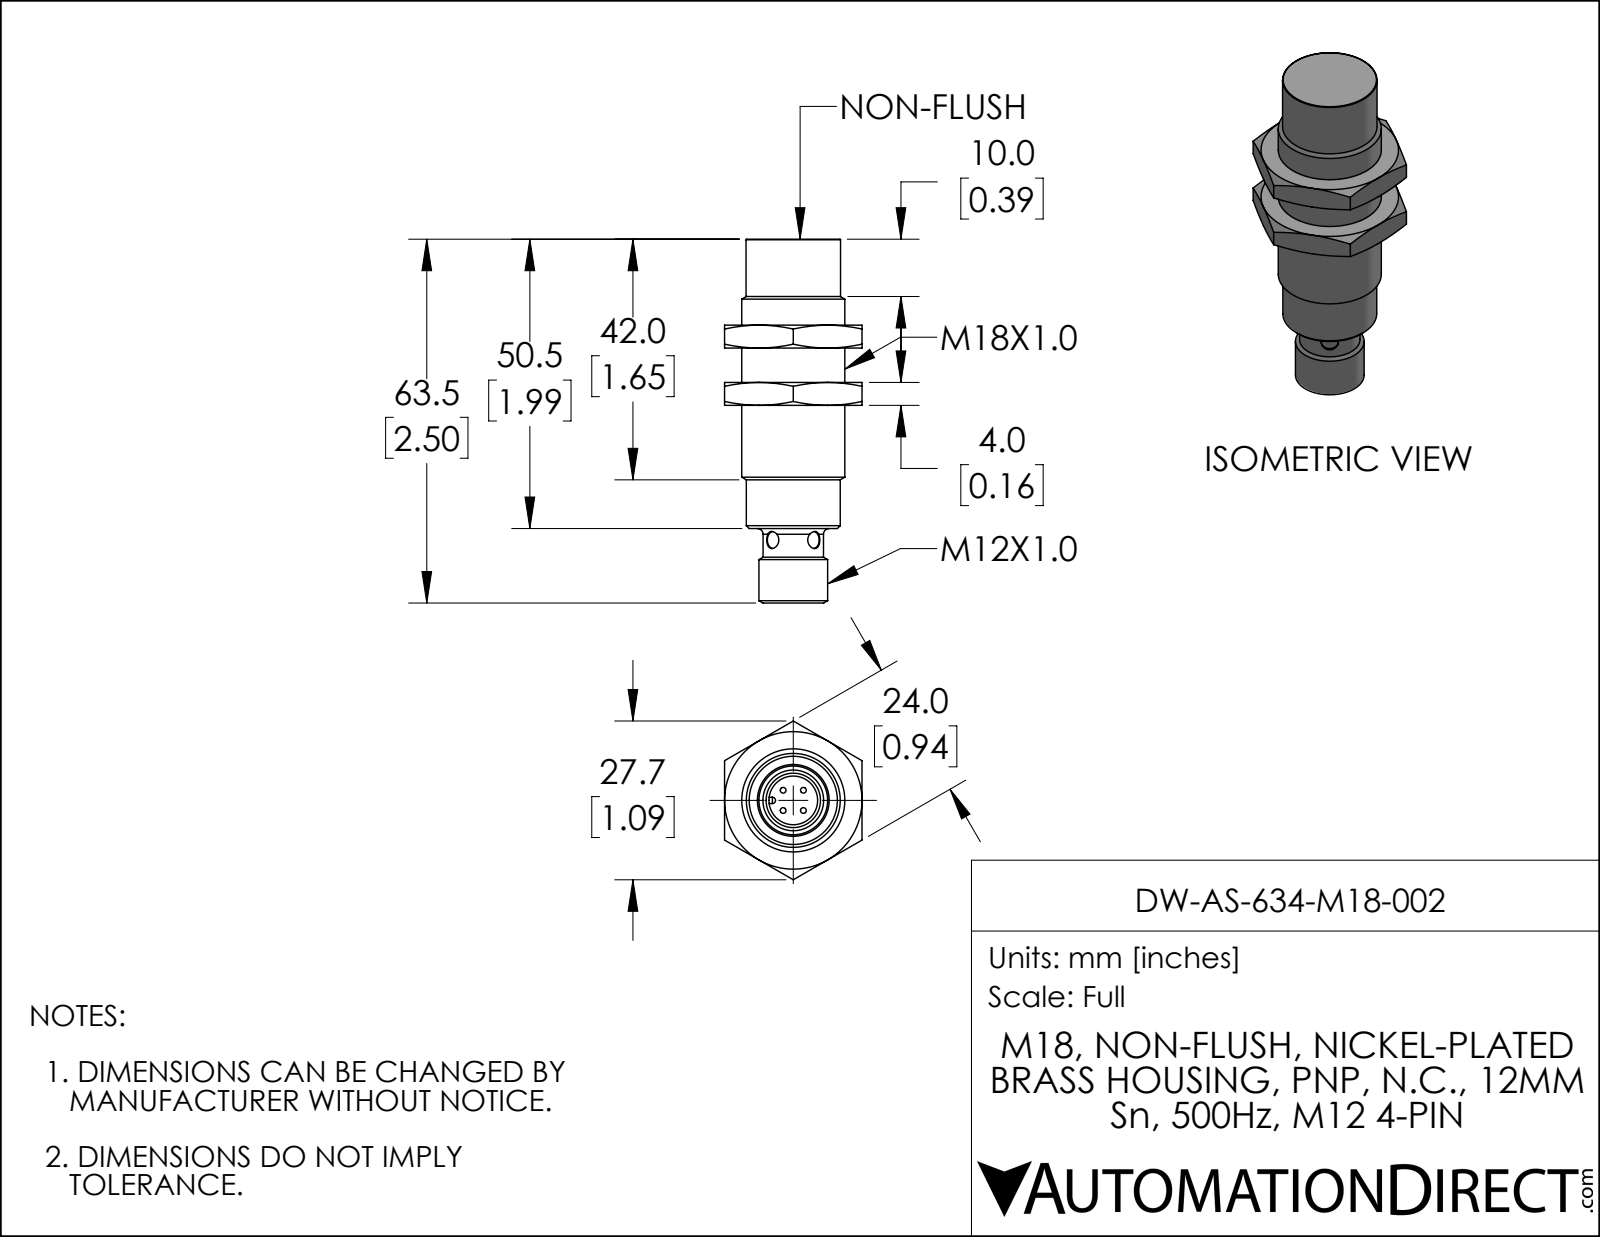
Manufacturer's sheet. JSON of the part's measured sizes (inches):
{"part_name": "DW-AS-634-M18-002", "step_written_by": "SolidWorks 2019 (AUTOMOTIVE_DESIGN)", "units": "inches", "bodies": {"solids": 1, "faces": 82, "planar": 27, "cylindrical": 18, "other": 37}, "overall_size": [2.5, 1.091, 0.945], "volume_in3": 0.905, "surface_area_in2": 8.005, "round_holes": [[0.118, 2], [0.335, 1]], "round_bosses_or_shafts": [[0.039, 4], [0.709, 1], [0.65, 1], [0.646, 1], [0.472, 1], [0.415, 1]], "partial_cylinders_radius": [[0.022, 2]], "face_to_face_distances": [0.394, 0.157, 0.945, 0.591, 0.748, 0.984, 1.142, 0.551, 0.236, 1.988]}
